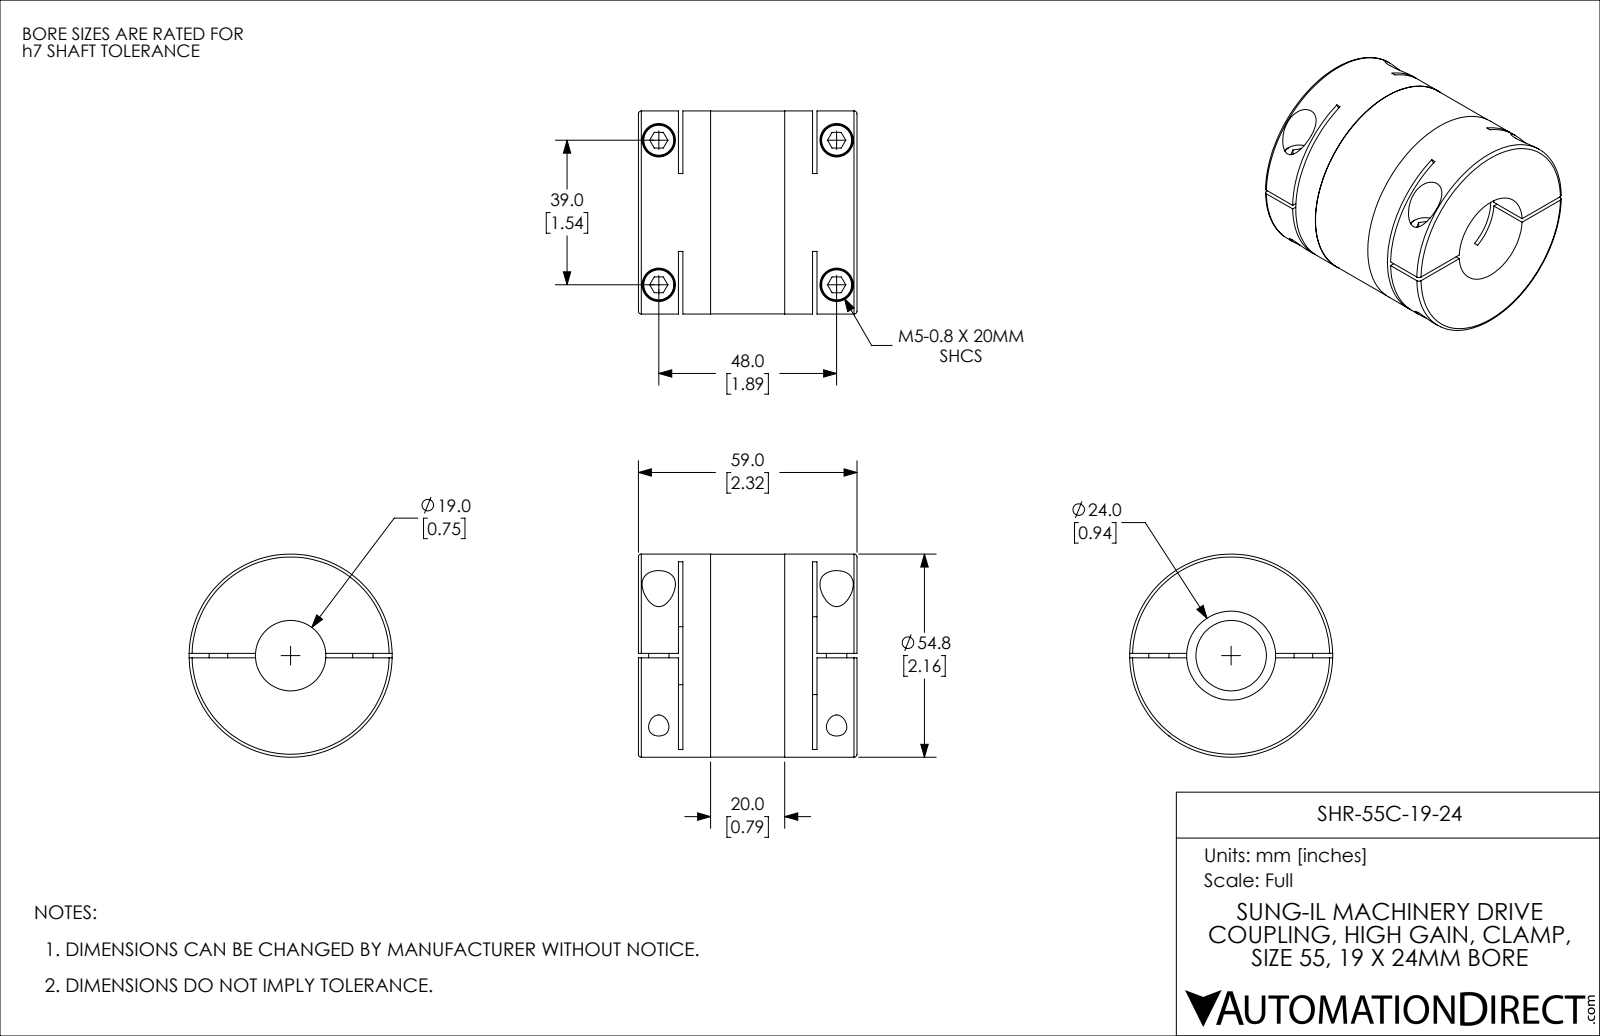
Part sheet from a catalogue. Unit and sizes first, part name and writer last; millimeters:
Units: millimetres
Overall size (bounding box): 59 × 54.8 × 54.8
Round holes (diameter × count): ⌀5.5 ×4, ⌀9 ×4, ⌀19 ×1, ⌀24 ×1, ⌀26 ×1
Round bosses / shafts (diameter × count): ⌀8.5 ×4, ⌀5 ×2, ⌀54.8 ×1, ⌀54.7 ×1
Partial cylindrical surfaces — rounded edges, fillets, slot ends (radius × count): R60 ×2
Main face-to-face distances: 1.2, 12, 47, 10.8, 48.2, 36.2, 59, 35, 37.4, 19.5
Hole centre spacings: 39, 48, 61.85
Volume: 106 888 mm³ · Surface area: 28 776 mm²
Bodies: 1 solid, 144 faces (70 planar, 58 cylindrical, 16 other)
Part name (STEP PRODUCT): SHR-55C-19-24
STEP written by: SolidWorks 2021 (CONFIG_CONTROL_DESIGN)
